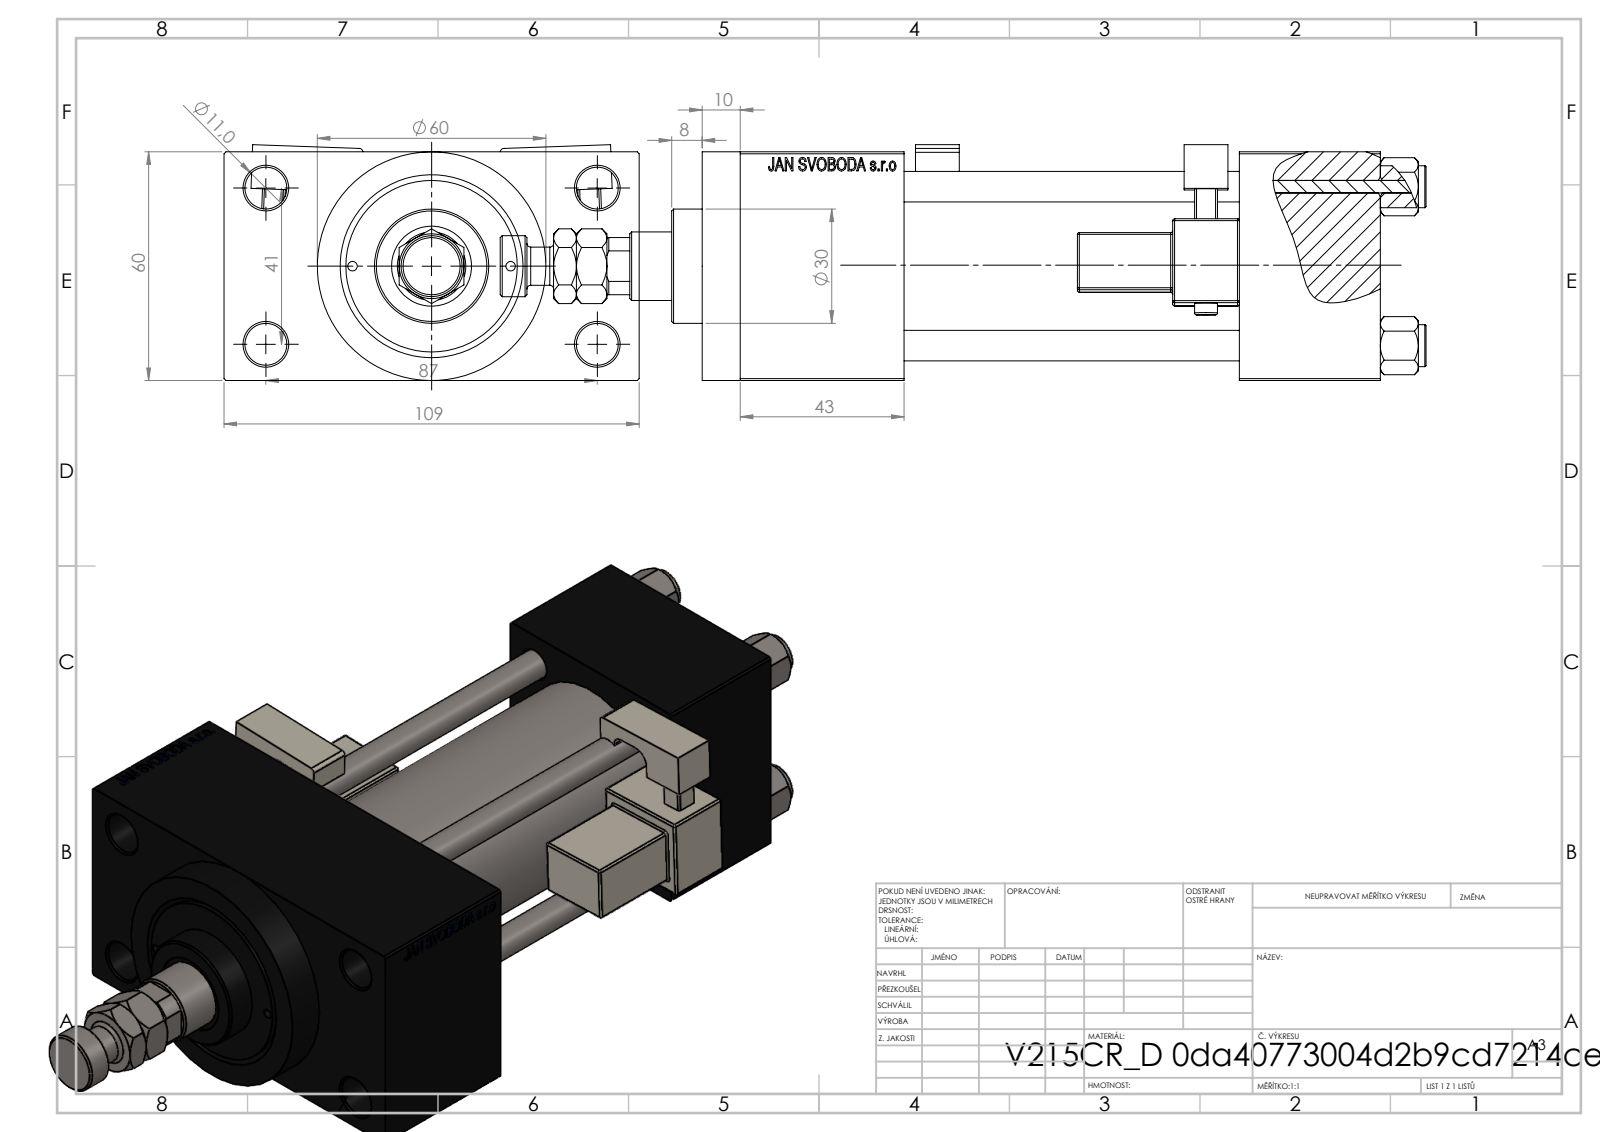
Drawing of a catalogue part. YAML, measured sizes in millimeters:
part_name: "NUT_M5_D; V215CR_VCP_D; V215_VC_A; V215CR_D_TYCINKA (+3 more)"
step_written_by: "SolidWorks 2019 (CONFIG_CONTROL_DESIGN)"
units: millimeters
bodies: {solids: 14, faces: 1318, planar: 574, cylindrical: 156, other: 588}
overall_size: [243, 109, 61.9]
volume: 584397
surface_area: 149473
round_holes:
  - {diameter: 8, count: 4}
  - {diameter: 11, count: 4}
  - {diameter: 2.5, count: 2}
  - {diameter: 7, count: 2}
  - {diameter: 16.66, count: 2}
  - {diameter: 24, count: 2}
  - {diameter: 8.5, count: 1}
  - {diameter: 18, count: 1}
  - {diameter: 21, count: 1}
  - {diameter: 31, count: 1}
  - {diameter: 40, count: 1}
  - {diameter: 45, count: 1}
round_bosses_or_shafts:
  - {diameter: 11, count: 4}
  - {diameter: 6, count: 2}
  - {diameter: 60, count: 1}
  - {diameter: 46, count: 1}
  - {diameter: 30, count: 1}
  - {diameter: 16, count: 1}
  - {diameter: 10, count: 1}
partial_cylinders:
  - {radius: 0.5, count: 48}
  - {radius: 1, count: 2}
  - {radius: 2.5, count: 2}
  - {radius: 4, count: 2}
  - {radius: 8.5, count: 1}
face_to_face_distances: [60, 88, 24.5, 84.5, 37, 125, 168, 131, 43, 53]
hole_center_spacings: [20.85, 22.65, 29.49, 30.62, 41.7, 46.53, 47.15, 48.09]
